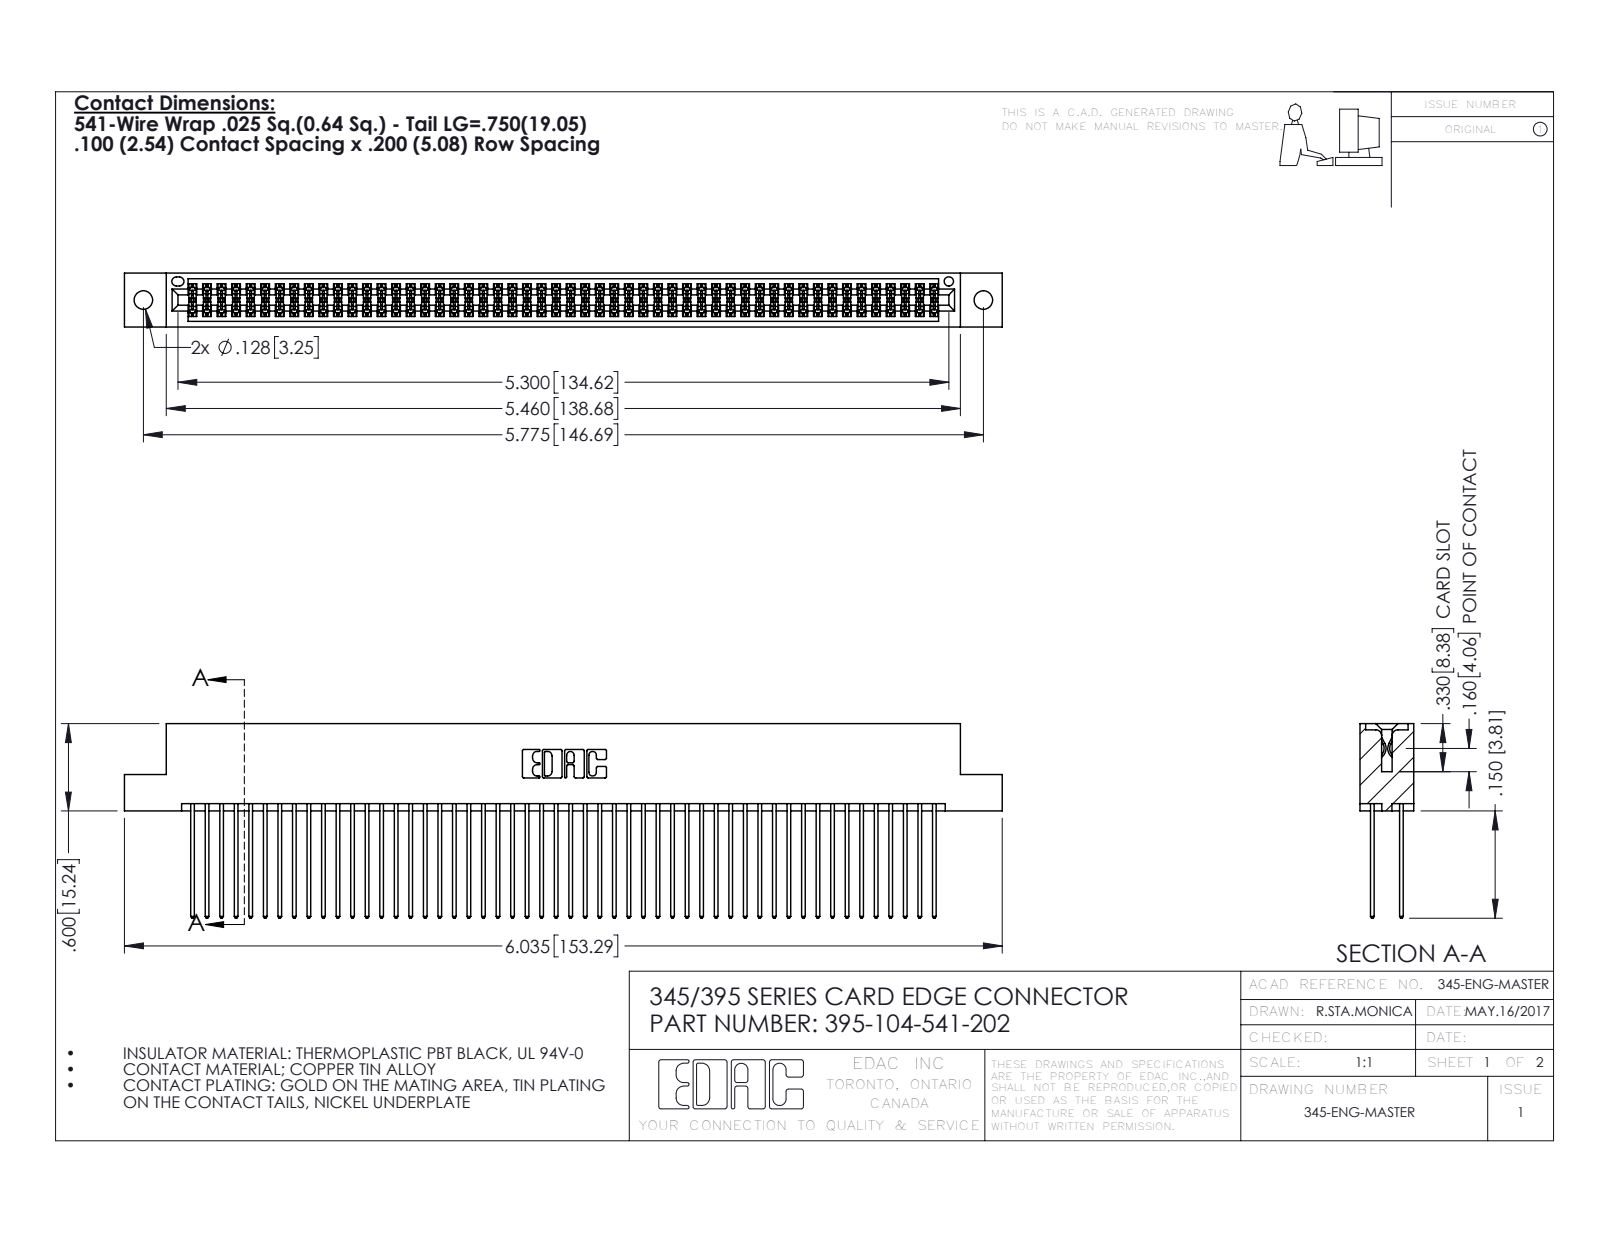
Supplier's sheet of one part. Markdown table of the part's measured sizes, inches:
| quantity | value |
| --- | --- |
| part name | 345 Part_Flush Mounting Lugs - 0.128 Dia; 395-104-541-202; 345-292-001_345-293-141 |
| STEP written by | SolidWorks 2016 (CONFIG_CONTROL_DESIGN) |
| units | inches |
| bodies | 105 solids, 5326 faces (3512 planar, 1814 cylindrical, 0 other) |
| overall size | 6.035 × 1.337 × 0.37 |
| volume | 0.949 in³ |
| surface area | 39.84 in² |
| round holes (diameter × count) | 0.128 × 2, 0.064 × 1 |
| partial cylindrical surfaces (radius × count) | 0.006 × 156, 0.01 × 104, 0.01 × 22, 0.007 × 6, 0.031 × 6, 0.026 × 3, 0.014 × 2, 0.019 × 2 |
| main face-to-face distances | 0.298, 0.072, 0.2, 0.098, 0.272, 0.025, 0.225, 0.37, 0.175, 0.149 |
| hole center spacings | 0.27, 5.539, 5.775 |
